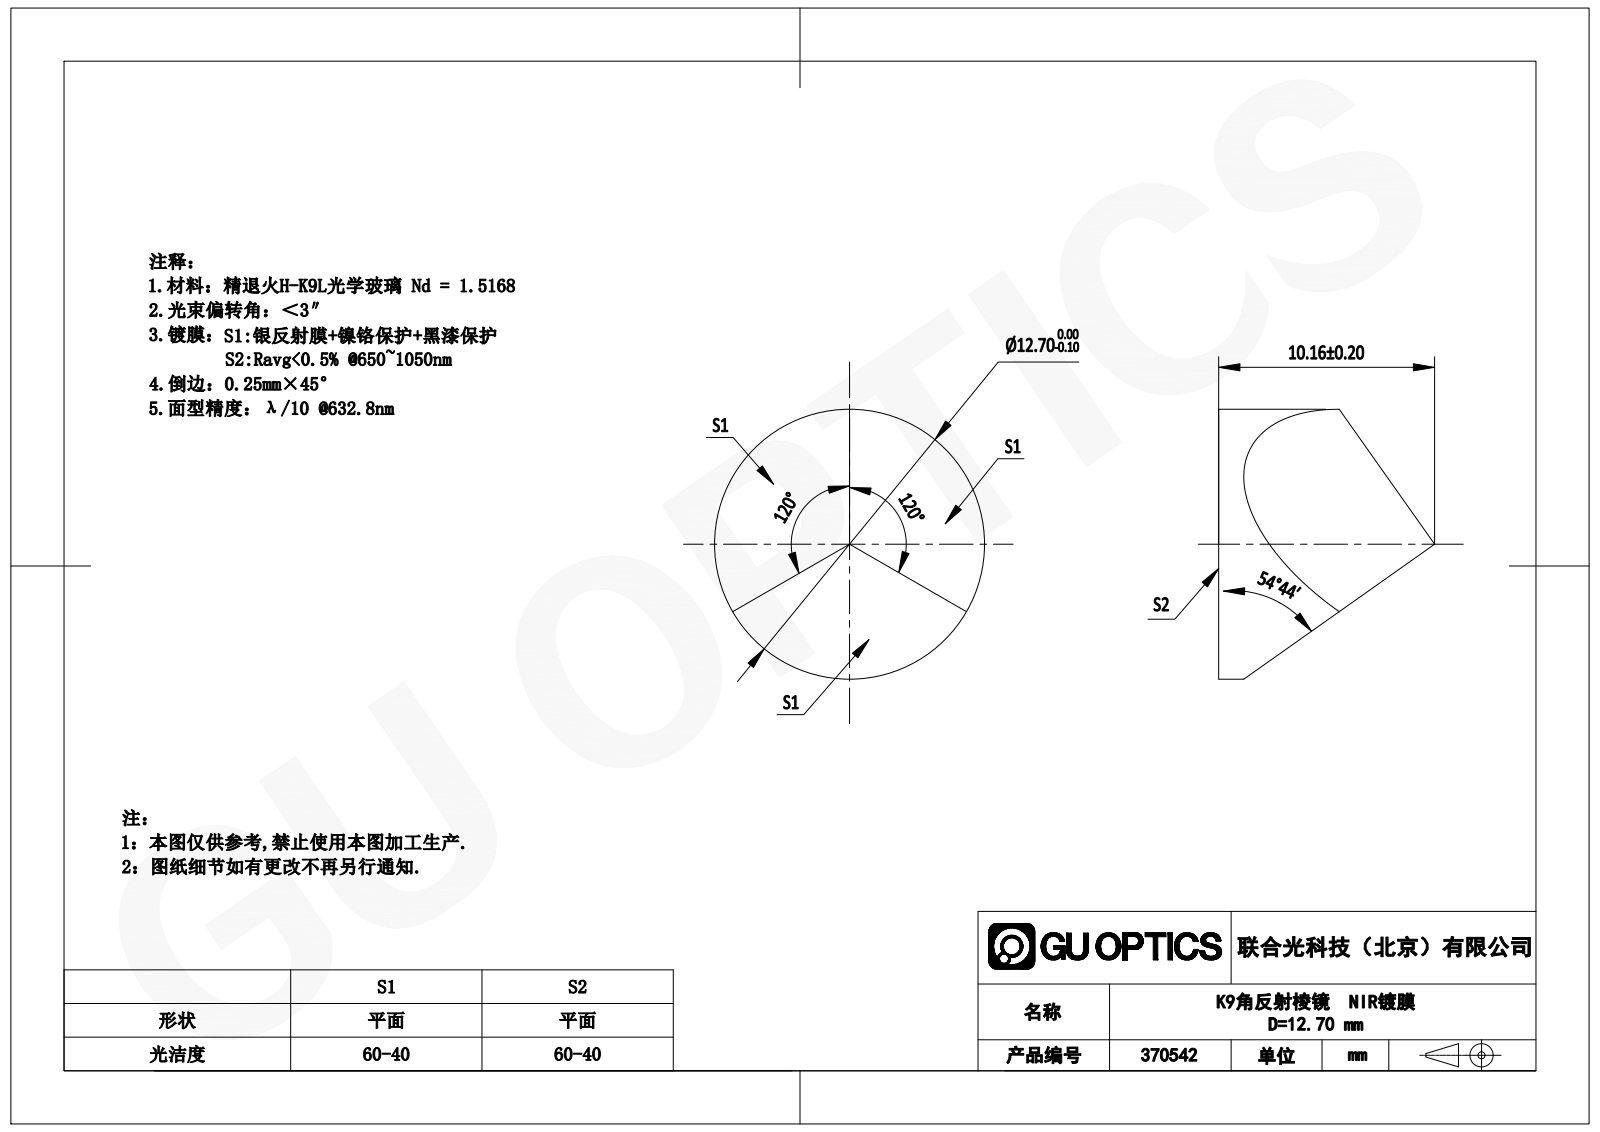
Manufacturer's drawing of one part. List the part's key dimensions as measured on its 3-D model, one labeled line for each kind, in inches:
Part name (STEP PRODUCT): GP16-012-1
STEP written by: SolidWorks 2022 (AUTOMOTIVE_DESIGN)
Units: inches
Bodies: 1 solid, 12 faces (8 planar, 2 cylindrical, 2 other)
Overall size (bounding box): 0.5 × 0.5 × 0.395
Volume: 0.04 in³ · Surface area: 0.699 in²
Round bosses / shafts (diameter × count): ⌀0.5 ×1
Main face-to-face distances: 0.395
